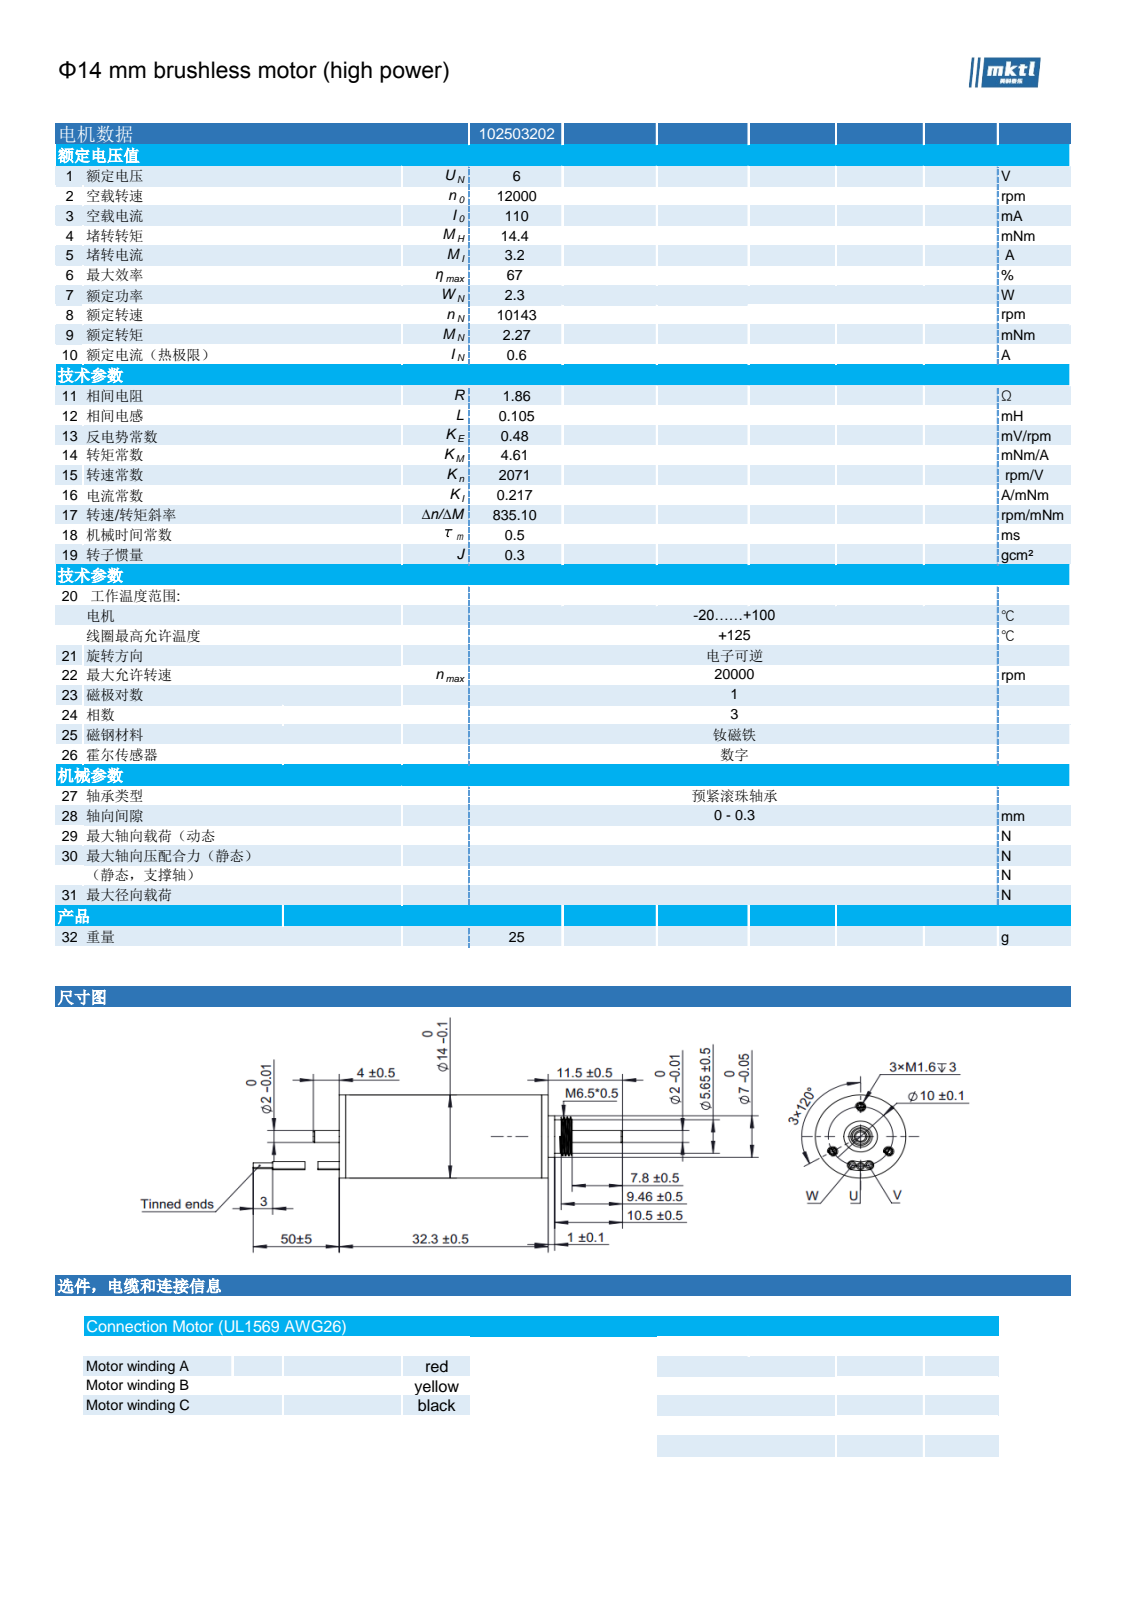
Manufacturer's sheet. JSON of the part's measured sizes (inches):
{"part_name": "102503202", "step_written_by": "SolidWorks 2025 (AUTOMOTIVE_DESIGN)", "units": "inches", "bodies": {"solids": 121, "faces": 849, "planar": 267, "cylindrical": 528, "other": 54}, "overall_size": [2.248, 0.551, 0.551], "volume_in3": 0.277, "surface_area_in2": 31.66, "round_holes": [[0.047, 3], [0.049, 3], [0.118, 1], [0.122, 1], [0.157, 1], [0.197, 1], [0.205, 1], [0.236, 1], [0.276, 1], [0.28, 1], [0.386, 1], [0.394, 1]], "round_bosses_or_shafts": [[0.047, 3], [0.031, 3], [0.023, 3], [0.551, 1], [0.52, 1], [0.516, 1], [0.26, 1], [0.256, 1]], "partial_cylinders_radius": [[0.03, 2], [0.167, 1], [0.226, 1]], "face_to_face_distances": [0.016, 0.024, 0.031, 0.039, 0.047, 0.055, 0.063, 0.071, 0.079, 0.087], "hole_center_spacings": [0.197, 0.341]}
